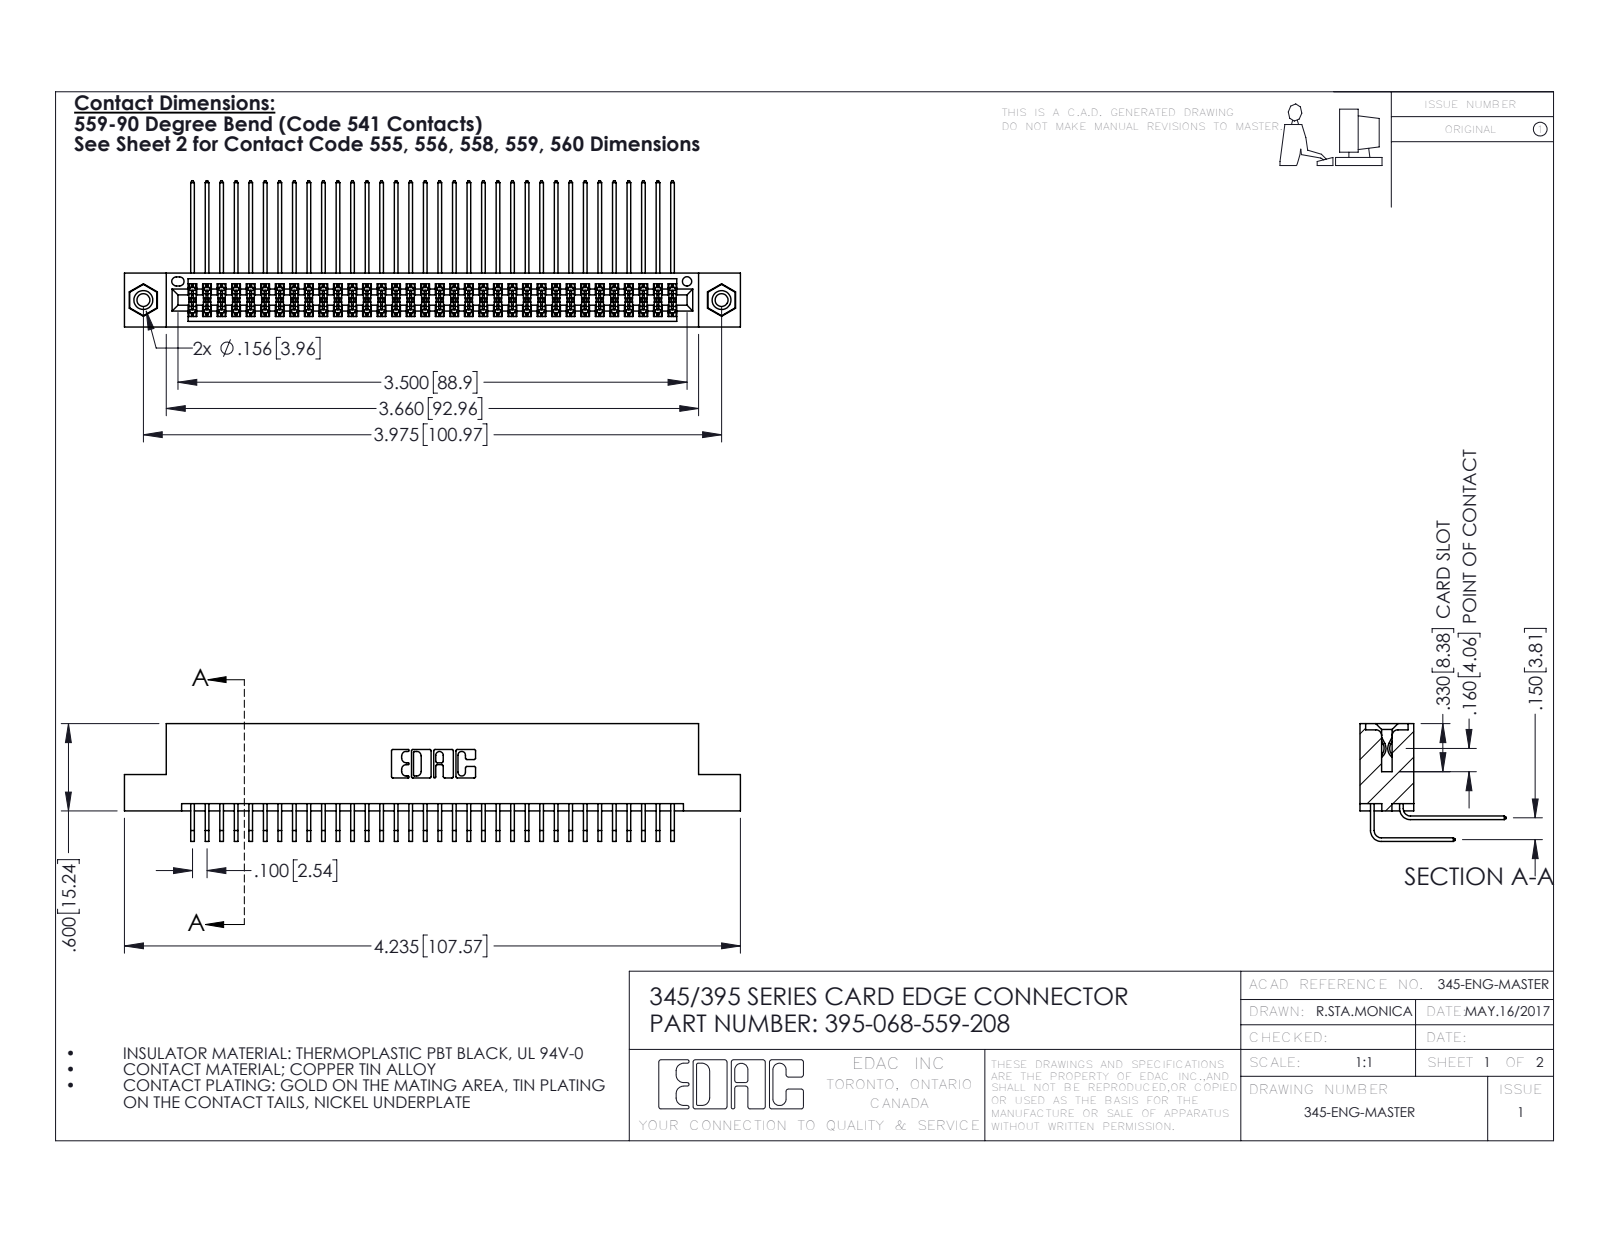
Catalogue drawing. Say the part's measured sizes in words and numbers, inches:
The part is named "395-068-559-208; 345-250-001_345-250-003-102; 345 Part_Flush Mounting Lugs - 0.156 Dia-TI; 345-292-001_559 Tail - 2 (+1 more)". Its 3-D file was written by "SolidWorks 2016 (CONFIG_CONTROL_DESIGN)". It is 71 solids with 3722 faces: 2492 planar, 1214 cylindrical and 16 other. Overall it measures 4.235 by 1.005 by 0.809 inches. Its volume is 0.657 cubic inches and its surface area 27.29 square inches. Round holes: 2 of diameter 0.089, 2 of diameter 0.125, 2 of diameter 0.156, 1 of diameter 0.064. Round bosses or shafts: 2 of diameter 0.155. Partial cylindrical surfaces (rounded edges, fillets, slot ends): 103 of radius 0.006, 22 of radius 0.01, 6 of radius 0.007, 6 of radius 0.031, 3 of radius 0.026, 2 of radius 0.014, 2 of radius 0.019, 2 of radius 0.022. The main face-to-face distances are 0.072, 0.298, 0.2, 0.37, 0.098, 0.272, 0.025, 0.225, 0.175, 0.15. The hole center spacings are 0.27, 3.74, 3.975.
